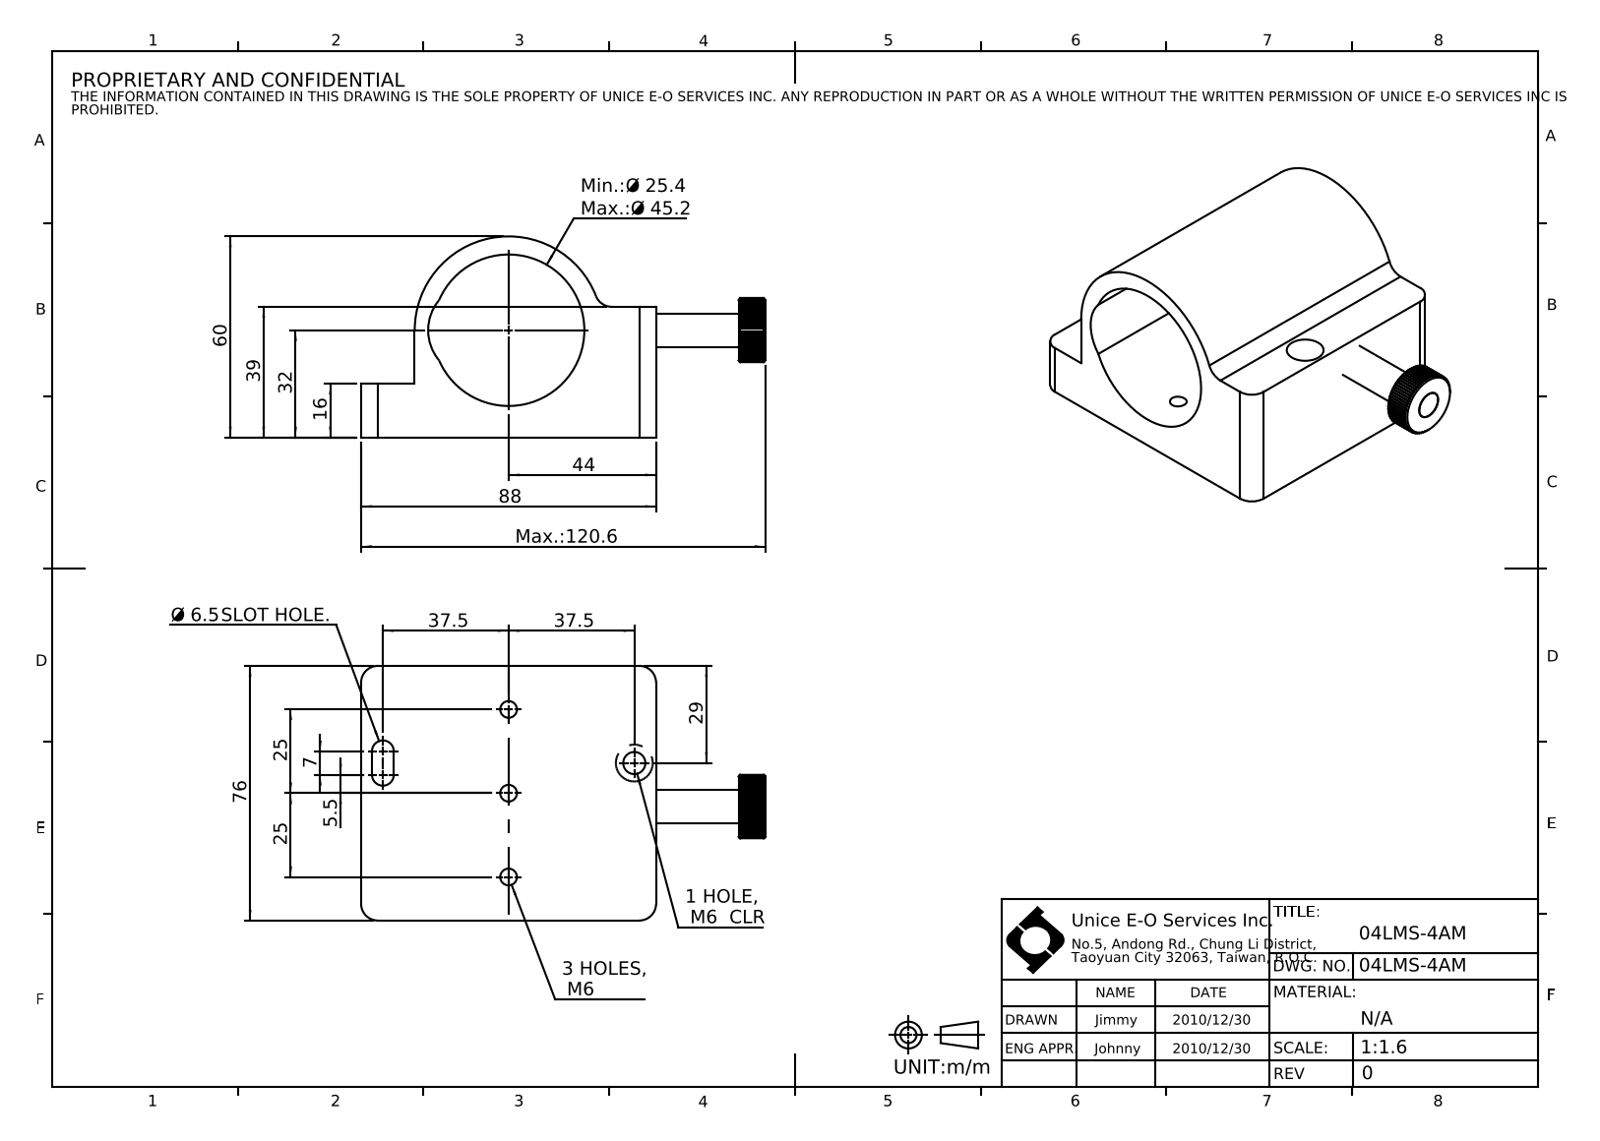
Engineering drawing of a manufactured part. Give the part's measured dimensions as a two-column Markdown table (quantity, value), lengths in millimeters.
| quantity | value |
| --- | --- |
| part name | 04LMS-4AM |
| STEP written by | SolidWorks 2016 (CONFIG_CONTROL_DESIGN) |
| units | millimeters |
| bodies | 3 solids, 238 faces (20 planar, 212 cylindrical, 6 other) |
| overall size | 120.6 × 76 × 60 |
| volume | 173 140 mm³ |
| surface area | 41 016 mm² |
| round holes (diameter × count) | 5 × 3, 6.6 × 1, 7.9 × 1, 8.5 × 1, 11 × 1, 45.2 × 1 |
| round bosses / shafts (diameter × count) | 10 × 1, 8 × 1, 6 × 1 |
| partial cylindrical surfaces (radius × count) | 0.1 × 72, 5 × 5, 3.25 × 2, 9.5 × 1, 14 × 1, 28 × 1 |
| main face-to-face distances | 16, 76, 72, 88, 39, 23, 32.6, 104.6, 120.6, 8 |
| hole center spacings | 25, 38.56, 40.77, 50, 50.62 |
